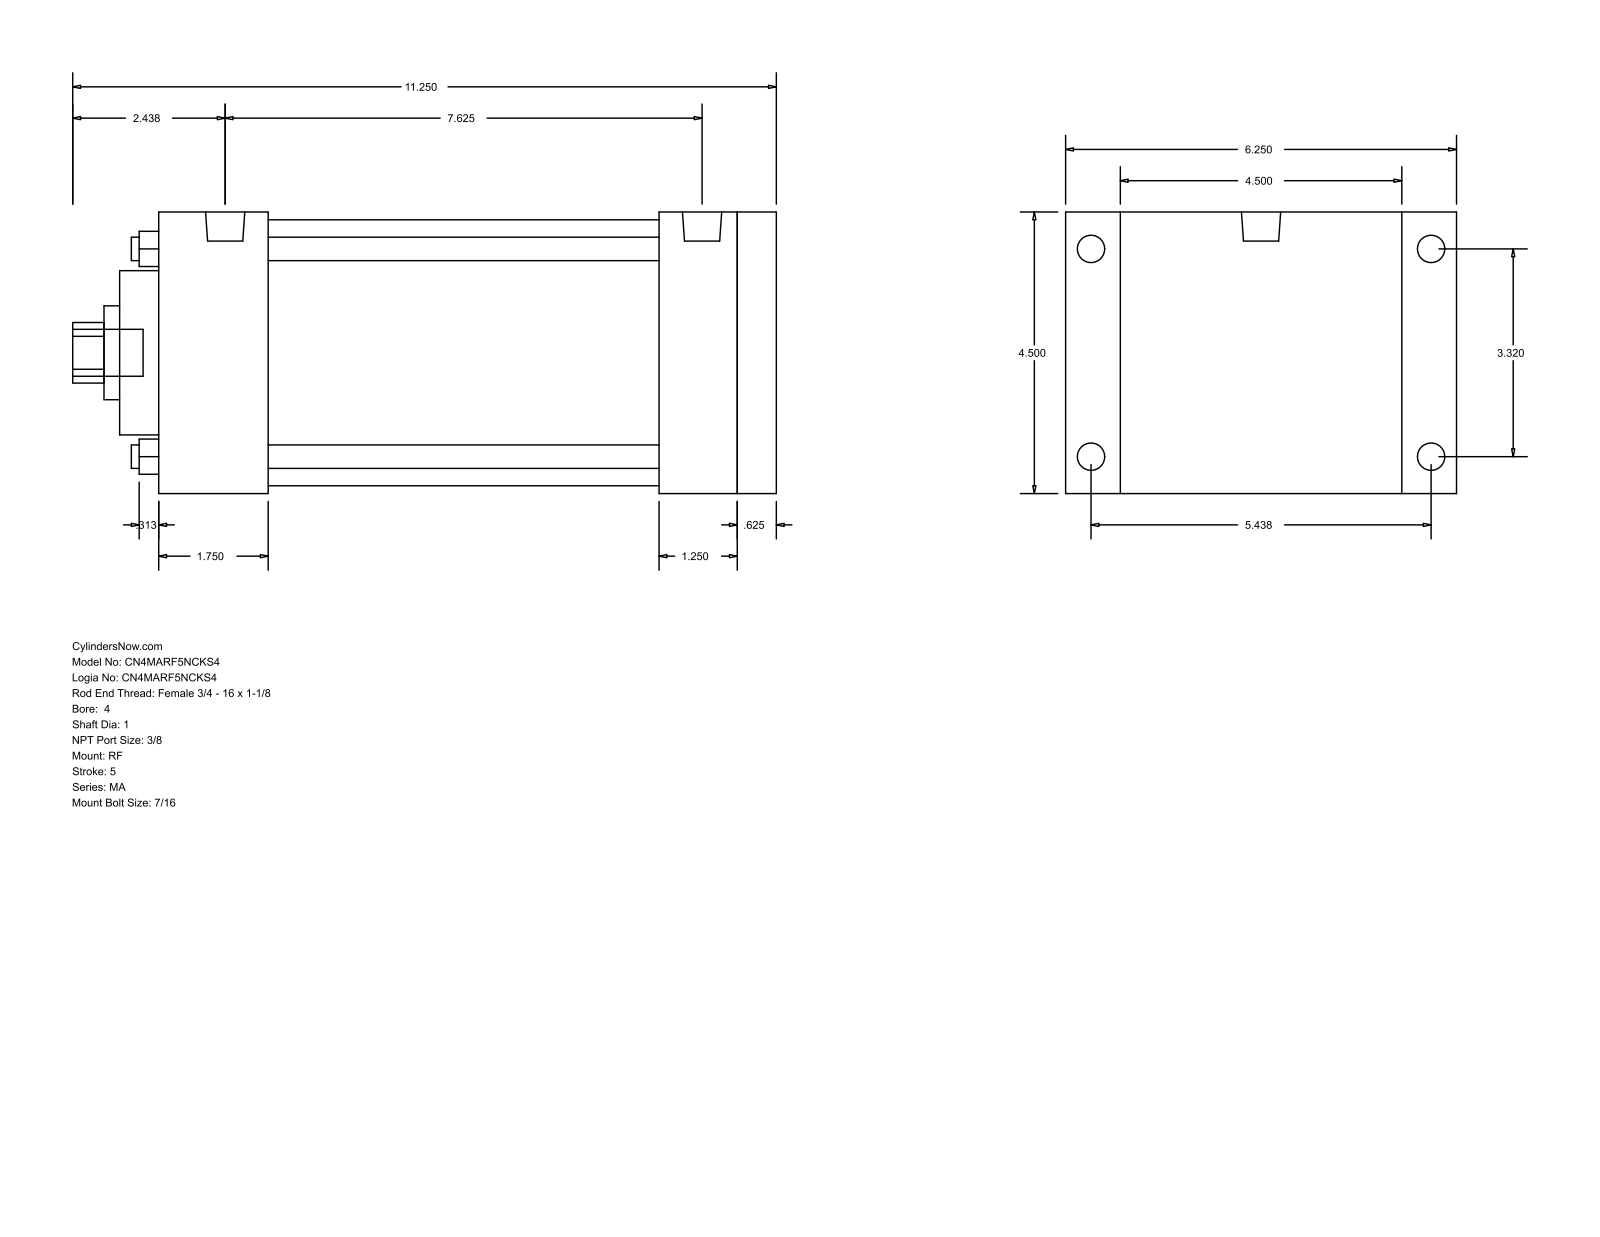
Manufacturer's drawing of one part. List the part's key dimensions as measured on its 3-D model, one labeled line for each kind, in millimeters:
Part name (STEP PRODUCT): MA_RF__0400_1
STEP written by: GSSL Pune (CONFIG_CONTROL_DESIGN)
Units: millimetres
Bodies: 0 solids, 94 faces (65 planar, 29 cylindrical, 0 other)
Overall size (bounding box): 285.75 × 158.75 × 114.3
Round holes (diameter × count): ⌀9.53 ×4, ⌀25.4 ×1, ⌀38.1 ×1, ⌀66.67 ×1, ⌀107.95 ×1
Round bosses / shafts (diameter × count): ⌀11.11 ×8, ⌀15.93 ×2, ⌀19.05 ×1
Partial cylindrical surfaces — rounded edges, fillets, slot ends (radius × count): R12.29 ×1
Main face-to-face distances: 114.3, 250.83, 15.87, 234.96, 22.23, 136.53, 203.2, 31.76, 47.63, 44.46
Hole centre spacings: 59.62, 84.32, 119.25
